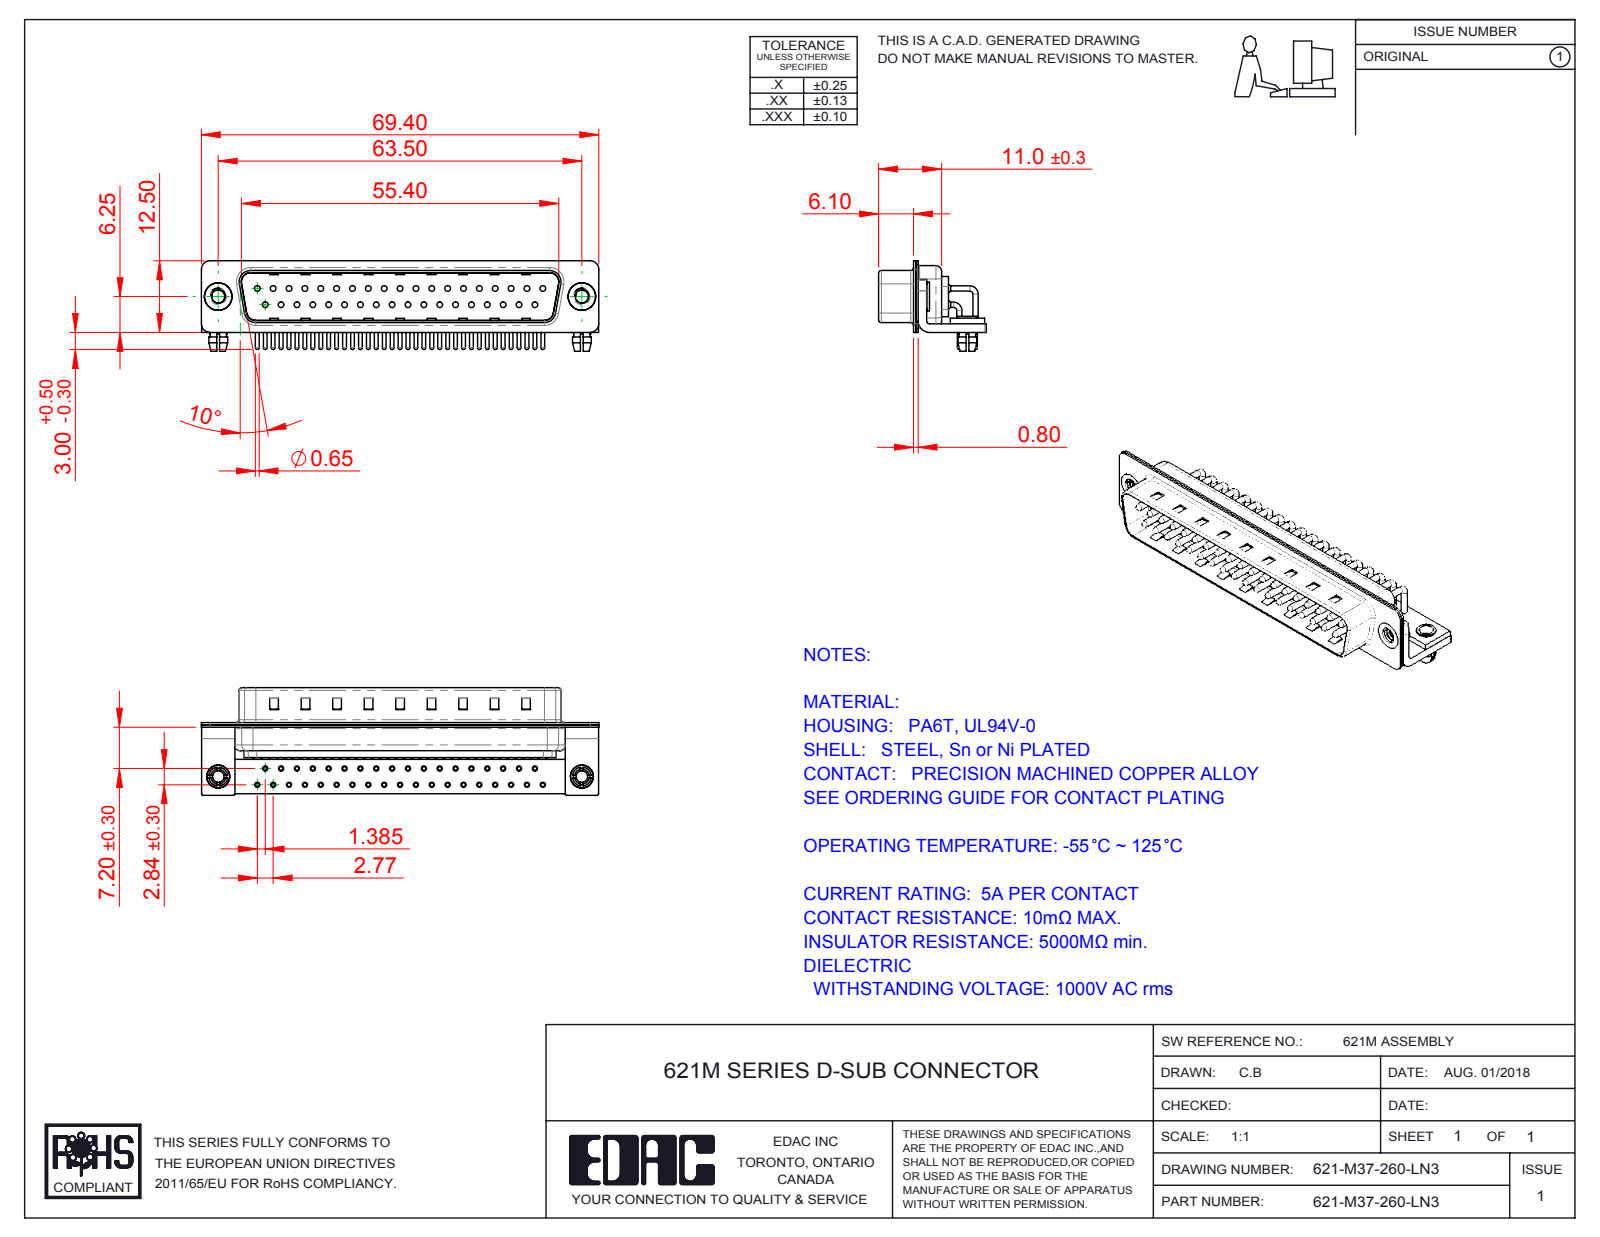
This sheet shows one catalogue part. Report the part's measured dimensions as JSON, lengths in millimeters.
{"part_name": "621M Contact Row 2; 621M Contact Row 1; 621M Shell Rear_37 Contacts; 621M Shell Front_37 Contacts (+6 more)", "step_written_by": "SolidWorks 2016 (CONFIG_CONTROL_DESIGN)", "units": "millimeters", "bodies": {"solids": 47, "faces": 4698, "planar": 2645, "cylindrical": 1601, "other": 452}, "overall_size": [69.4, 18.8, 15.8], "volume_mm3": 4643, "surface_area_mm2": 12155, "round_holes": [[2, 39], [0.9, 37], [1, 37], [1.7, 37], [2.26, 2], [2.5, 2], [3.2, 2], [4, 2], [4.8, 2]], "round_bosses_or_shafts": [[0.9, 46], [1.5, 37], [0.65, 37], [5, 2], [4.9, 2], [4, 2], [3.4, 2], [3.3, 2]], "partial_cylinders_radius": [[1.01, 37], [0.25, 16], [1.5, 16], [2, 13], [0.5, 9], [1.6, 8], [0.6, 4], [0.65, 4]], "face_to_face_distances": [0.4, 0.85, 1.25, 9.55, 1.5, 10.4, 8.3, 0.8, 8.7, 1], "hole_center_spacings": [3.16, 2.77, 5.54, 8.31, 11.08, 13.85, 5.03, 16.62]}
